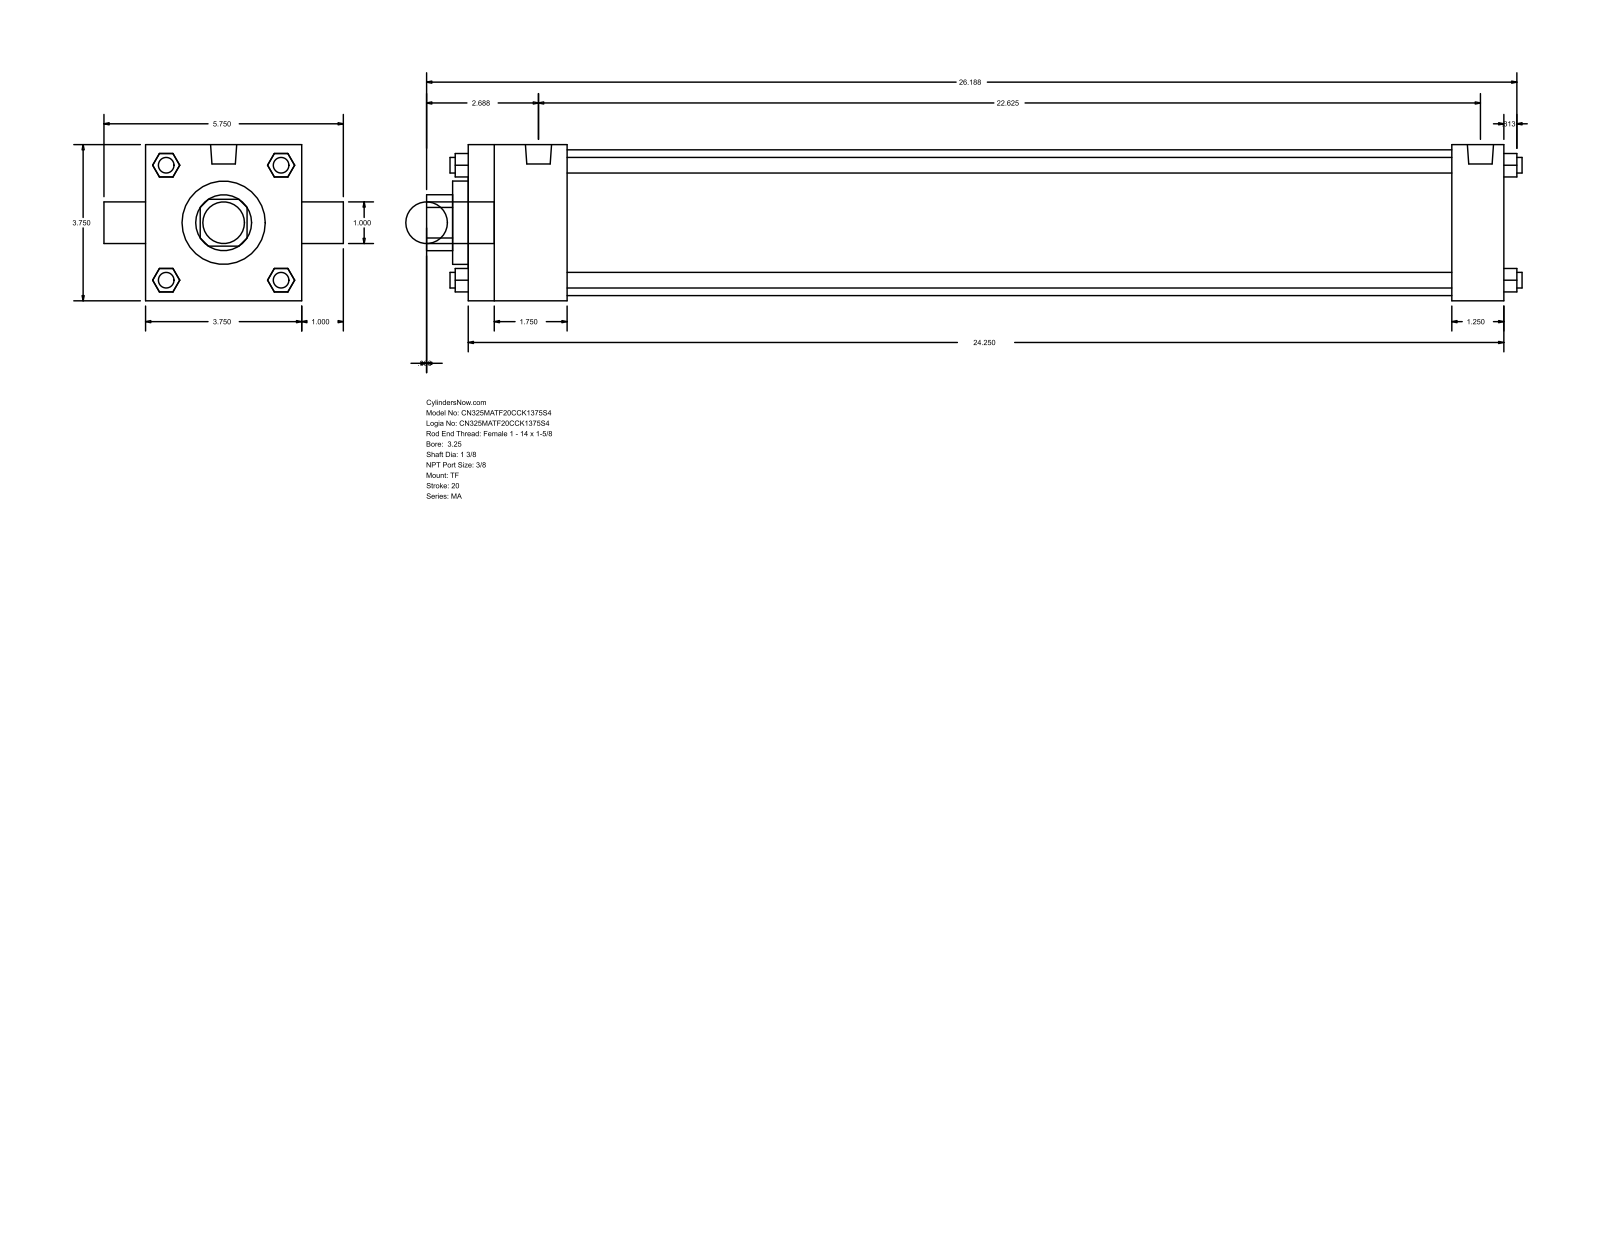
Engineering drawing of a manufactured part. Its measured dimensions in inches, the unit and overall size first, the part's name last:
Units: inches
Overall size (bounding box): 26.313 × 5.75 × 3.75
Round holes (diameter × count): ⌀1 ×1, ⌀1.375 ×1, ⌀2 ×1, ⌀3.5 ×1
Round bosses / shafts (diameter × count): ⌀0.375 ×4, ⌀0.437 ×3, ⌀0.627 ×2, ⌀1 ×1
Partial cylindrical surfaces — rounded edges, fillets, slot ends (radius × count): R0.672 ×1
Main face-to-face distances: 3.75, 24.875, 2.375, 23.625, 21.25, 22.5, 1.25, 0.375, 2.75, 24
Bodies: 0 solids, 120 faces (92 planar, 28 cylindrical, 0 other)
Part name (STEP PRODUCT): MA_TF__0325_1.375
STEP written by: GSSL Pune (CONFIG_CONTROL_DESIGN)
